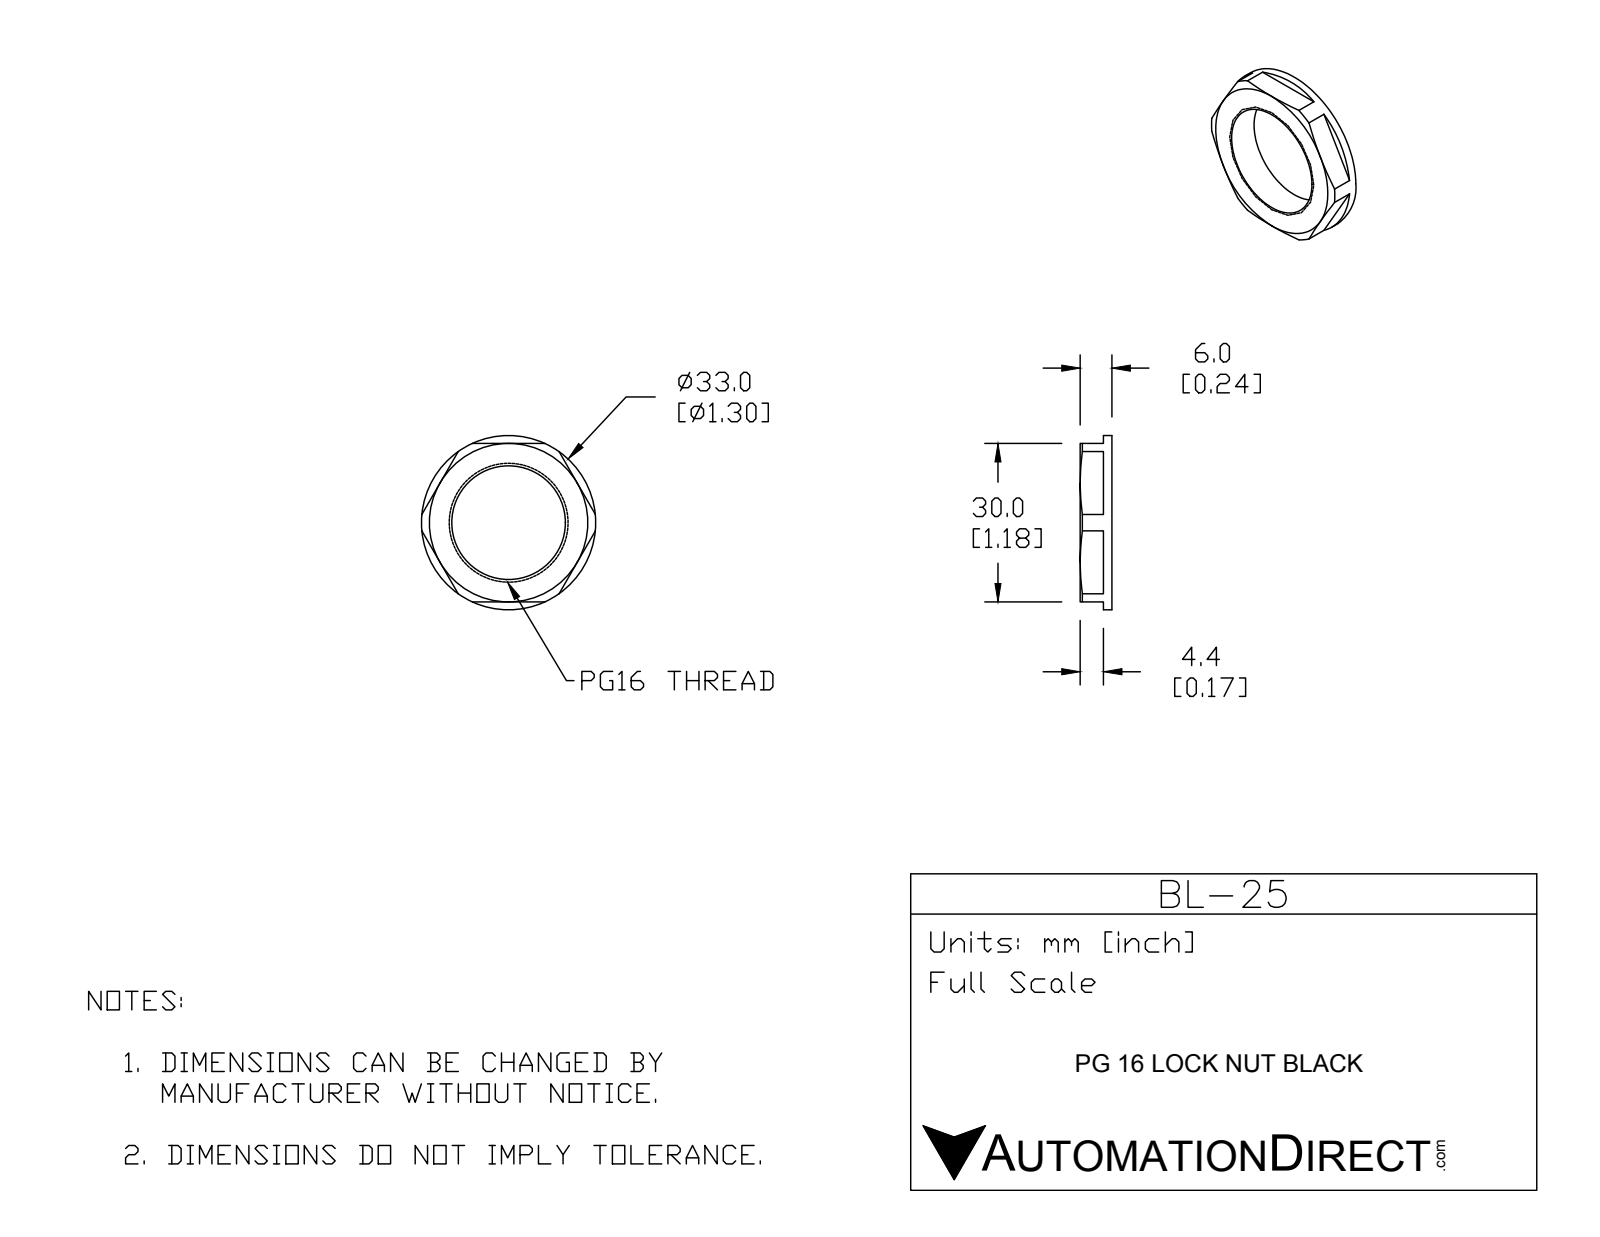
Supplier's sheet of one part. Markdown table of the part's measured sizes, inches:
| quantity | value |
| --- | --- |
| part name | BL-25 |
| STEP written by | SolidWorks 2015 (CONFIG_CONTROL_DESIGN) |
| units | inches |
| bodies | 1 solid, 33 faces (17 planar, 10 cylindrical, 6 other) |
| overall size | 1.299 × 1.299 × 0.236 |
| volume | 0.157 in³ |
| surface area | 3.081 in² |
| round holes (diameter × count) | 0.059 × 3, 0.846 × 1 |
| round bosses / shafts (diameter × count) | 1.299 × 1 |
| main face-to-face distances | 0.236, 1.181, 0.063, 0.173, 0.051, 0.224 |
| hole center spacings | 0.593, 1.026, 0.592, 1.026 |
